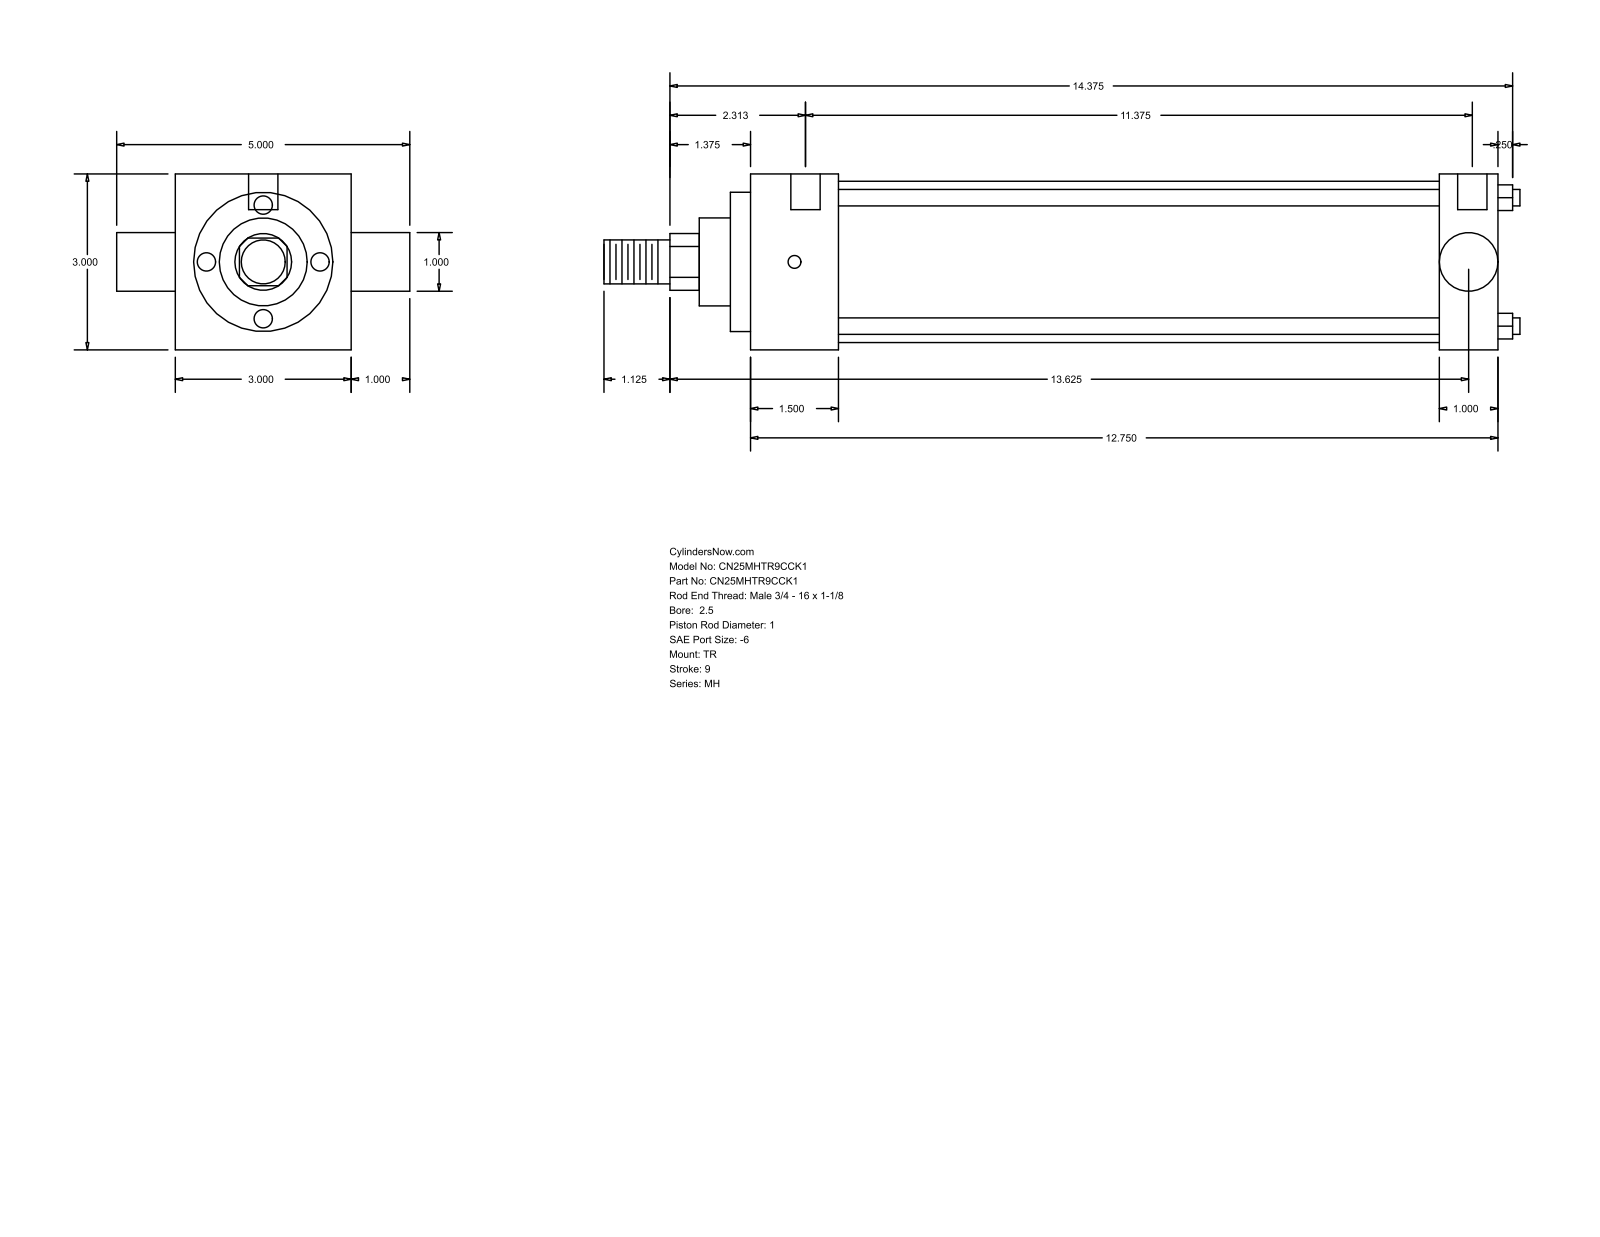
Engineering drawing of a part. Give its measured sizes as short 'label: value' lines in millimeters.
name: MH_TR__0250_1
written by: GSSL Pune (CONFIG_CONTROL_DESIGN)
unit: mm
bodies: 0 solids, 86 faces (61 planar, 25 cylindrical, 0 other)
size: 396.88 × 127 × 76.2
holes: 3× ⌀5.56, 2× ⌀12.7
bosses: 4× ⌀7.14, 1× ⌀69.85, 1× ⌀60.33, 1× ⌀38.1, 1× ⌀25.4, 1× ⌀25.35, 1× ⌀19.05
rounds: 1× R12.29
face distances: 76.2, 323.85, 25.39, 38.11, 285.74, 298.46, 260.35, 8.73, 46.84, 307.19
hole spacings: 3.18, 4.76, 288.92, 292.1, 293.68, 296.86
